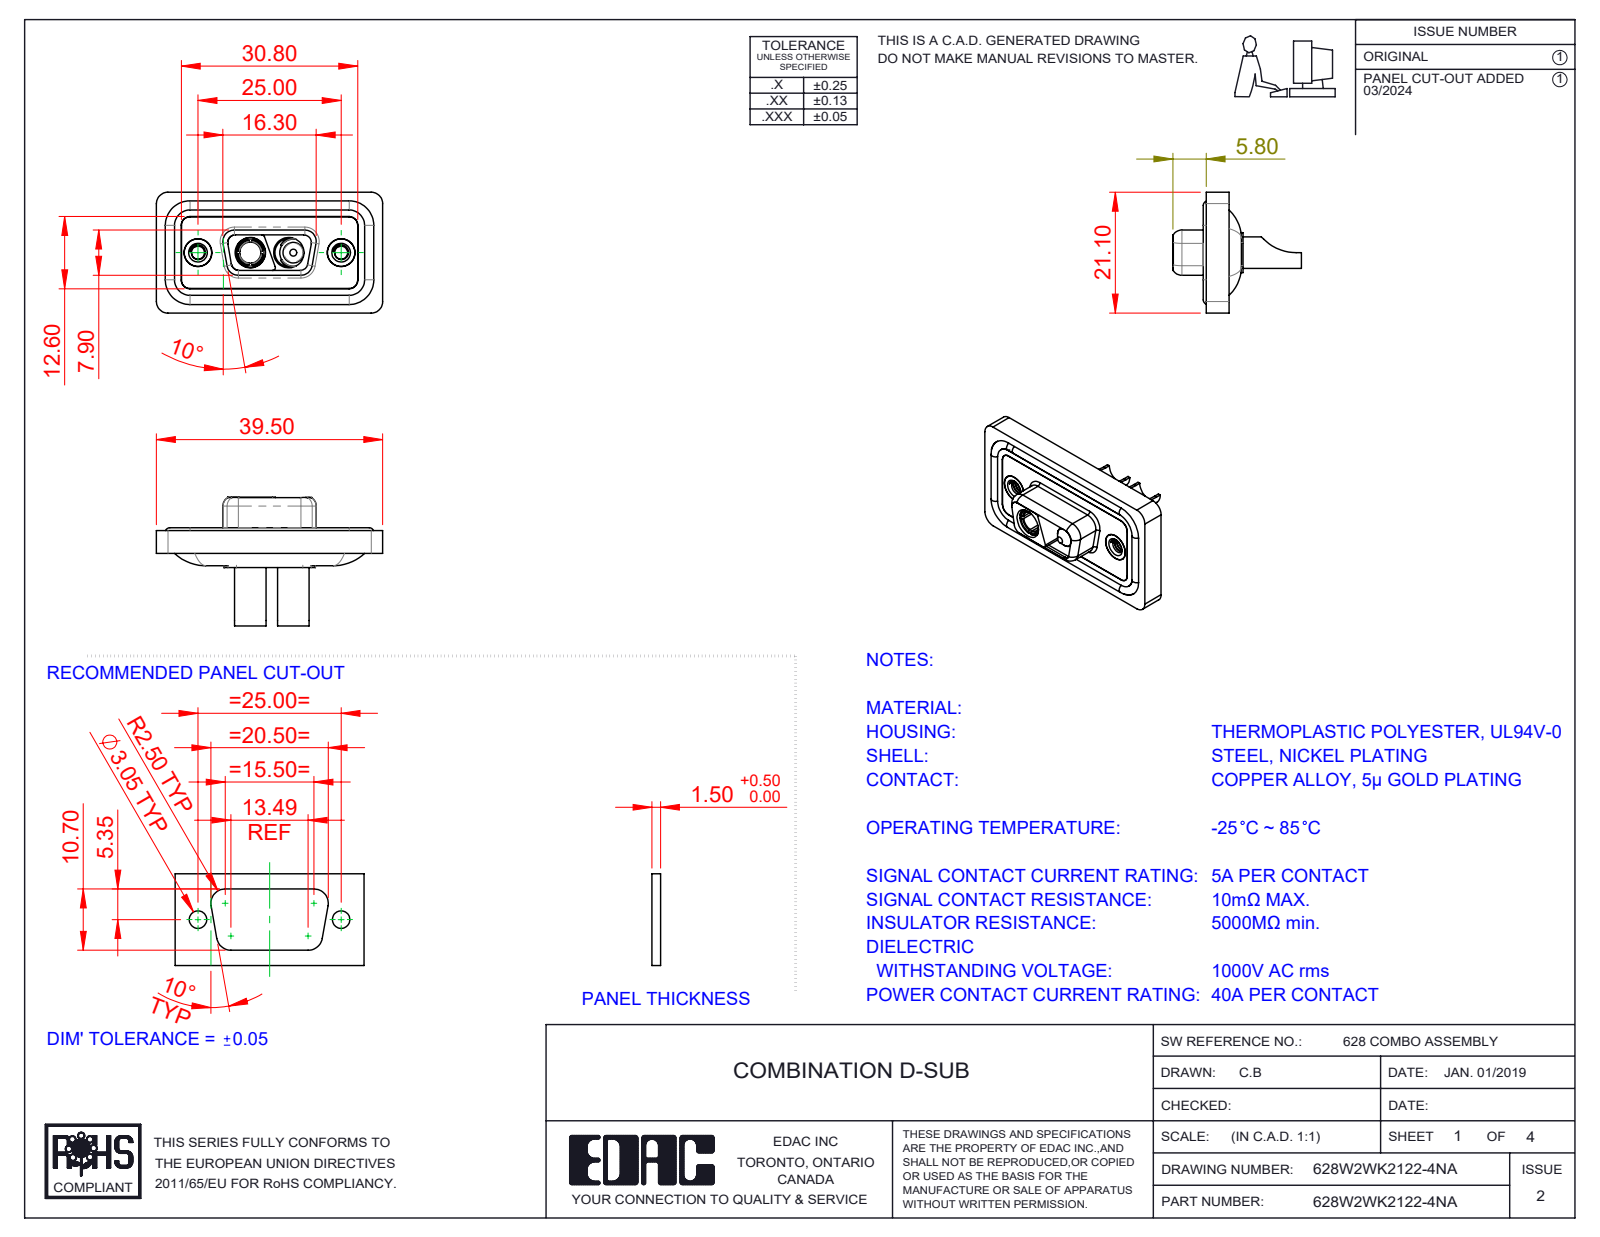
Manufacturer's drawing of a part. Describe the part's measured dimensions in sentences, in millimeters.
The part is named "628Combo Shell Rear_09 Contacts; 628Combo Waterproof Housing_09 Contacts; Power Socket_40A SC; 628Combo Housing_2WK2 (+4 more)". Its 3-D file was written by "SolidWorks 2023 (CONFIG_CONTROL_DESIGN)". It is 11 solids with 504 faces: 148 planar, 235 cylindrical and 121 other. Overall it measures 39.5 by 22.45 by 21.1 millimeters. Its volume is 4 684 cubic millimeters and its surface area 7 621 square millimeters. Round holes: 4 of diameter 4.85, 2 of diameter 2.26, 2 of diameter 4, 2 of diameter 4.05, 2 of diameter 4.6, 2 of diameter 5, 2 of diameter 5.3, 1 of diameter 3.7. Round bosses or shafts: 4 of diameter 1.6, 2 of diameter 5.5, 2 of diameter 5.2, 2 of diameter 4.95, 2 of diameter 4.8, 2 of diameter 4.75, 2 of diameter 3.75, 1 of diameter 4.96. Partial cylindrical surfaces (rounded edges, fillets, slot ends): 22 of radius 1.5, 18 of radius 2, 8 of radius 1.35, 8 of radius 1.6, 6 of radius 0.5, 4 of radius 0.25, 4 of radius 0.6, 4 of radius 0.65. The main face-to-face distances are 0.4, 1.1, 2.9, 1.6, 0.5, 1.8, 5.65, 5.35, 3.1, 0.7. The hole center spacings are 9.14, 15.86, 6.72, 25.
